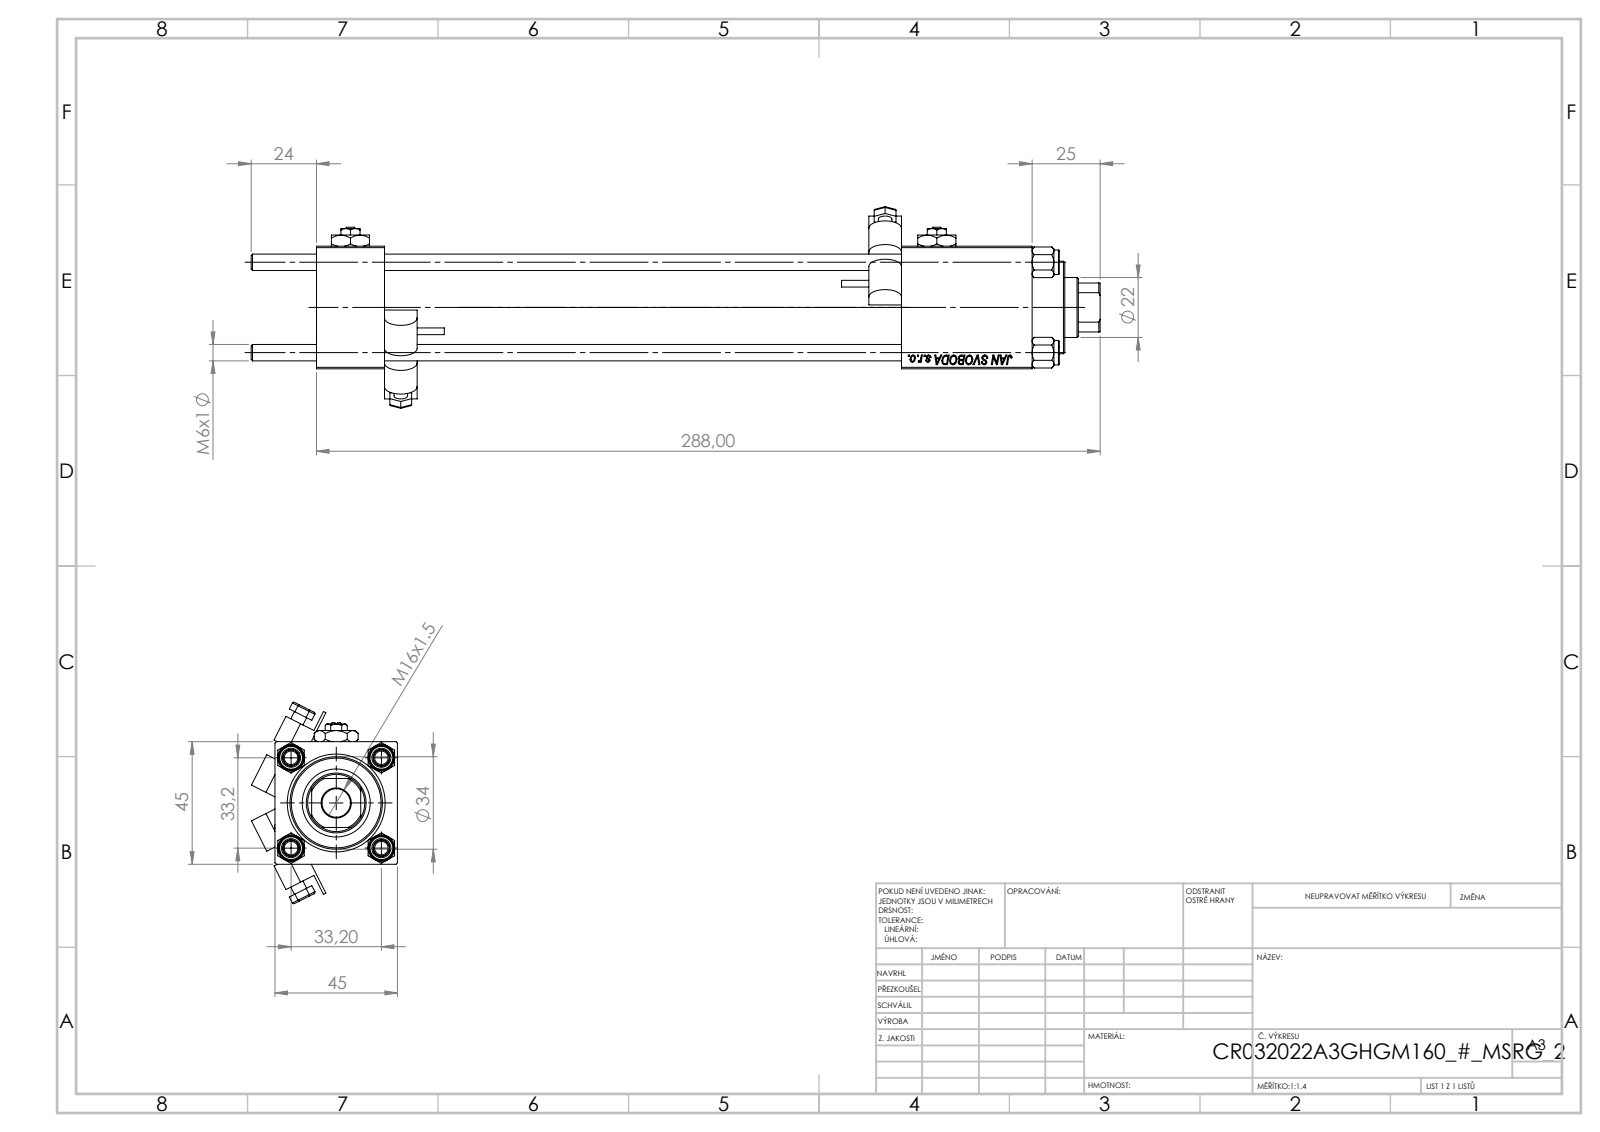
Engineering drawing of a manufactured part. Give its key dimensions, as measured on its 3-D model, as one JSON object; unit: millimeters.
{"part_name": "NUT_M5; Zatka_pro_OIL_PORT; V215_VC_A; V215CR_VCP (+3 more)", "step_written_by": "SolidWorks 2019 (CONFIG_CONTROL_DESIGN)", "units": "millimeters", "bodies": {"solids": 15, "faces": 1296, "planar": 602, "cylindrical": 116, "other": 578}, "overall_size": [312, 74.05, 53.66], "volume_mm3": 334908, "surface_area_mm2": 134099, "round_holes": [[6, 4], [7, 2], [13.16, 2], [20, 2], [10.5, 1], [22, 1], [24, 1], [25, 1], [32, 1], [33, 1]], "round_bosses_or_shafts": [[9, 4], [5, 2], [2.5, 2], [38, 1], [34, 1]], "partial_cylinders_radius": [[0.5, 12], [6, 4], [10.5, 1]], "face_to_face_distances": [45, 25, 215, 190, 263, 238, 48, 44.8, 234.3, 209.3], "hole_center_spacings": [23.48, 33.2, 46.95, 215.5]}
